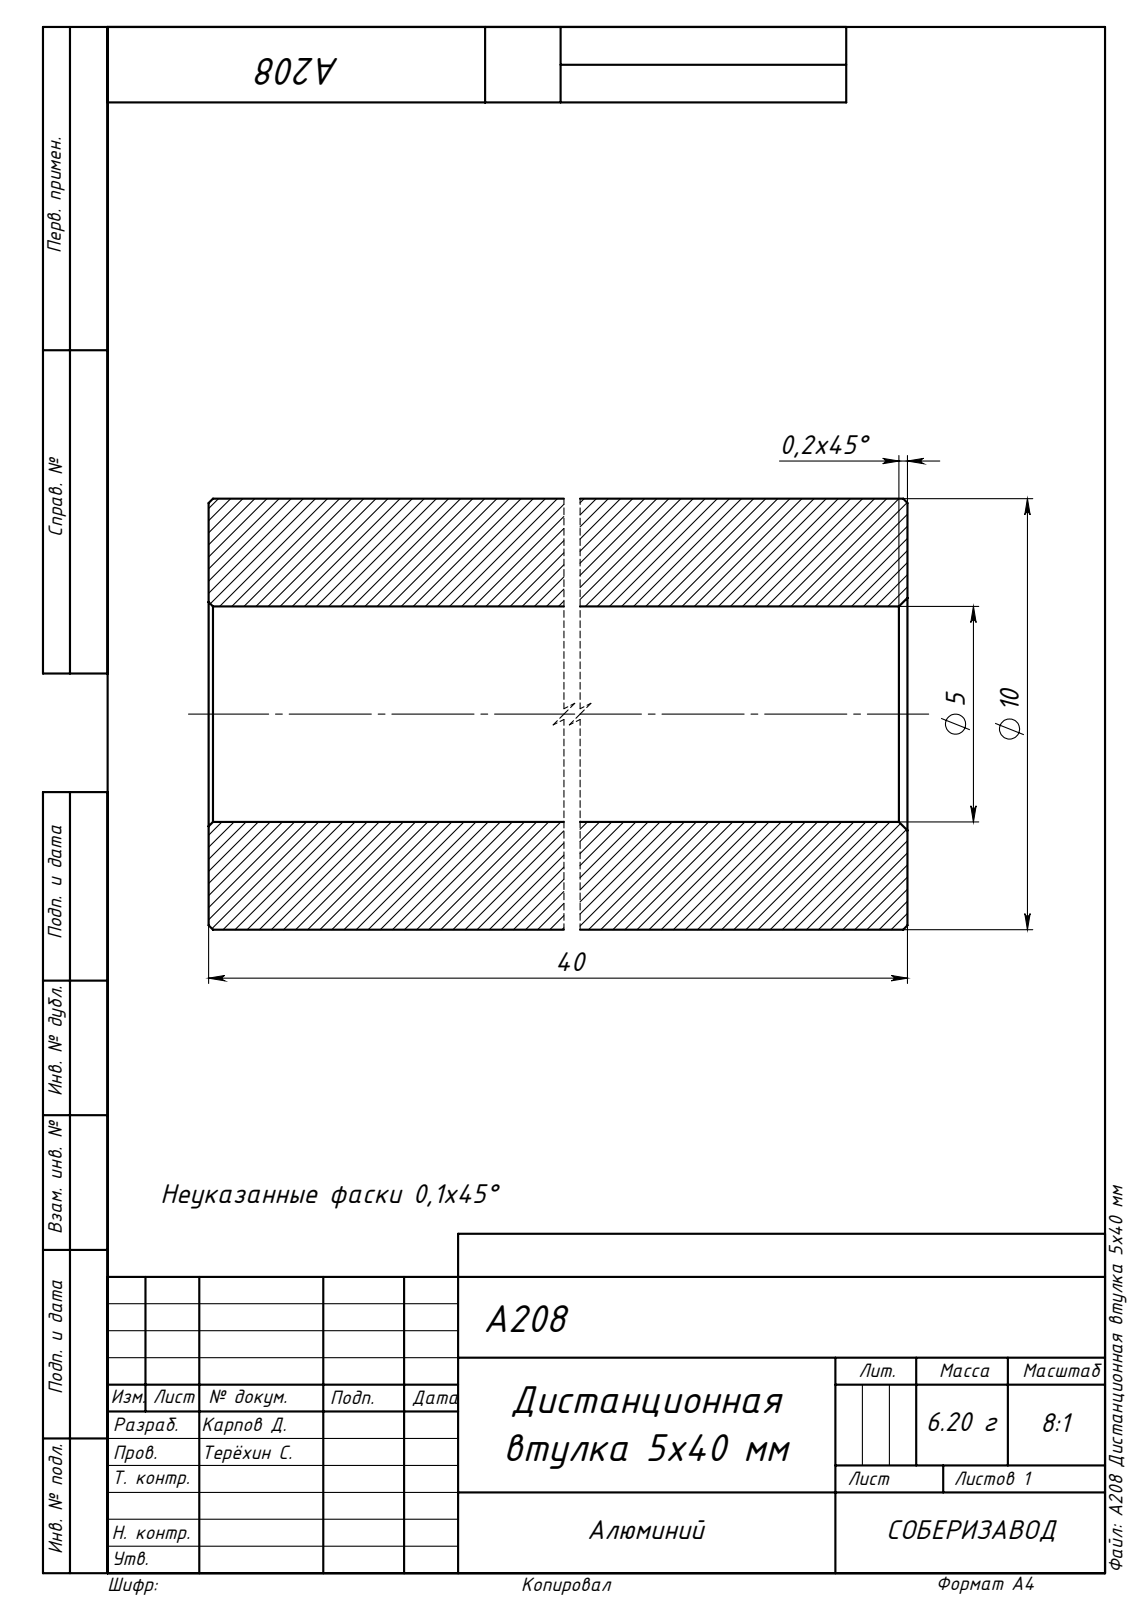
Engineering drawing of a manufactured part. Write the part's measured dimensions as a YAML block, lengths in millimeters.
part_name: "A208 Дистанционная втулка 5х40 мм"
step_written_by: "SolidWorks 2020 (AUTOMOTIVE_DESIGN)"
units: millimeters
bodies: {solids: 1, faces: 14, planar: 2, cylindrical: 4, other: 8}
overall_size: [40, 10, 10]
volume: 2355
surface_area: 1996
round_holes:
  - {diameter: 5, count: 1}
round_bosses_or_shafts:
  - {diameter: 10, count: 1}
face_to_face_distances: [40]
